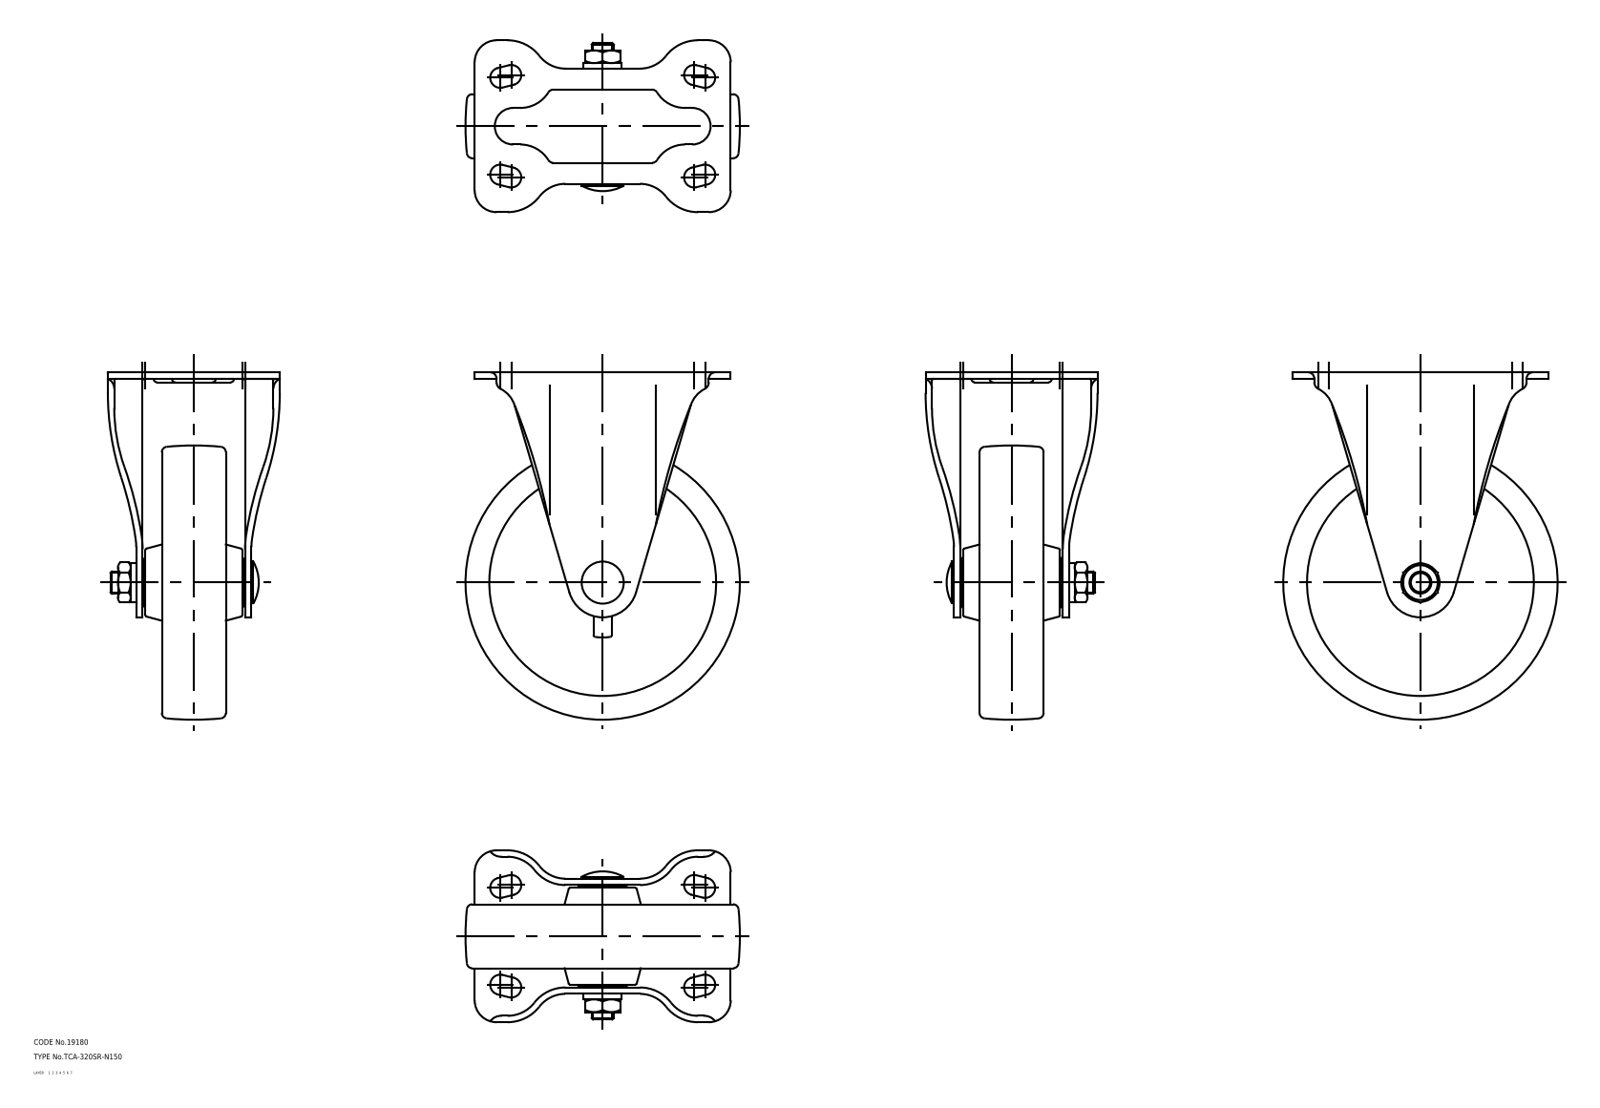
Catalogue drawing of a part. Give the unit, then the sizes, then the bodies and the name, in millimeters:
Units: millimetres
Overall size (bounding box): 190 × 150 × 94
Volume: 623 698 mm³ · Surface area: 124 463 mm²
Bodies: 3 solids, 214 faces (0 planar, 0 cylindrical, 214 other)
Part name (STEP PRODUCT): 67122329; 67122342; 67122355
STEP written by: CADfix (AUTOMOTIVE_DESIGN)
